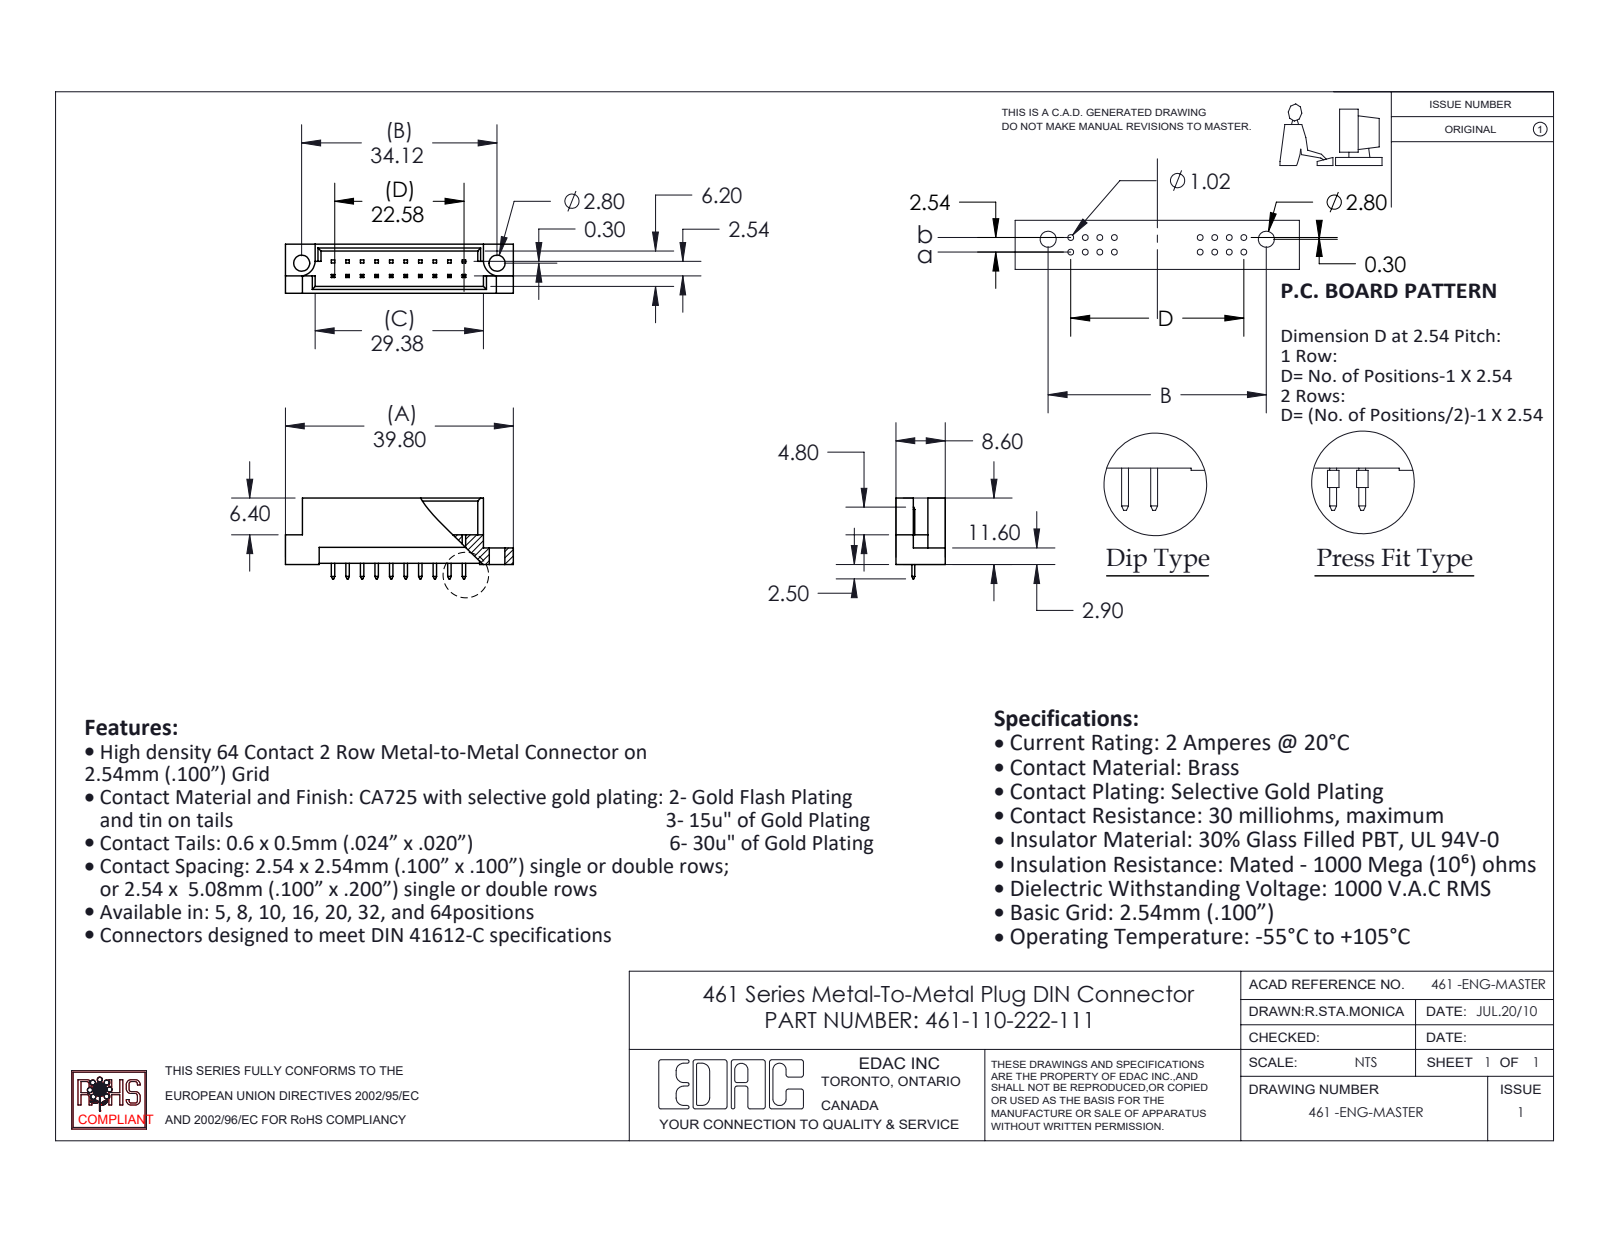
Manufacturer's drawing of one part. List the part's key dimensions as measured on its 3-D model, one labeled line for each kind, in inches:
Part name (STEP PRODUCT): 461-110-222-111; 461-290_22; 461 Part_20
STEP written by: SolidWorks 2020 (CONFIG_CONTROL_DESIGN)
Units: inches
Bodies: 11 solids, 268 faces (262 planar, 6 cylindrical, 0 other)
Overall size (bounding box): 1.567 × 0.555 × 0.339
Volume: 0.118 in³ · Surface area: 4.044 in²
Round holes (diameter × count): ⌀0.11 ×2
Partial cylindrical surfaces — rounded edges, fillets, slot ends (radius × count): R0.11 ×2
Main face-to-face distances: 0.047, 0.291, 0.339, 0.244, 0.1, 0.197, 0.129, 0.209, 0.082, 0.162
Hole centre spacings: 1.343
